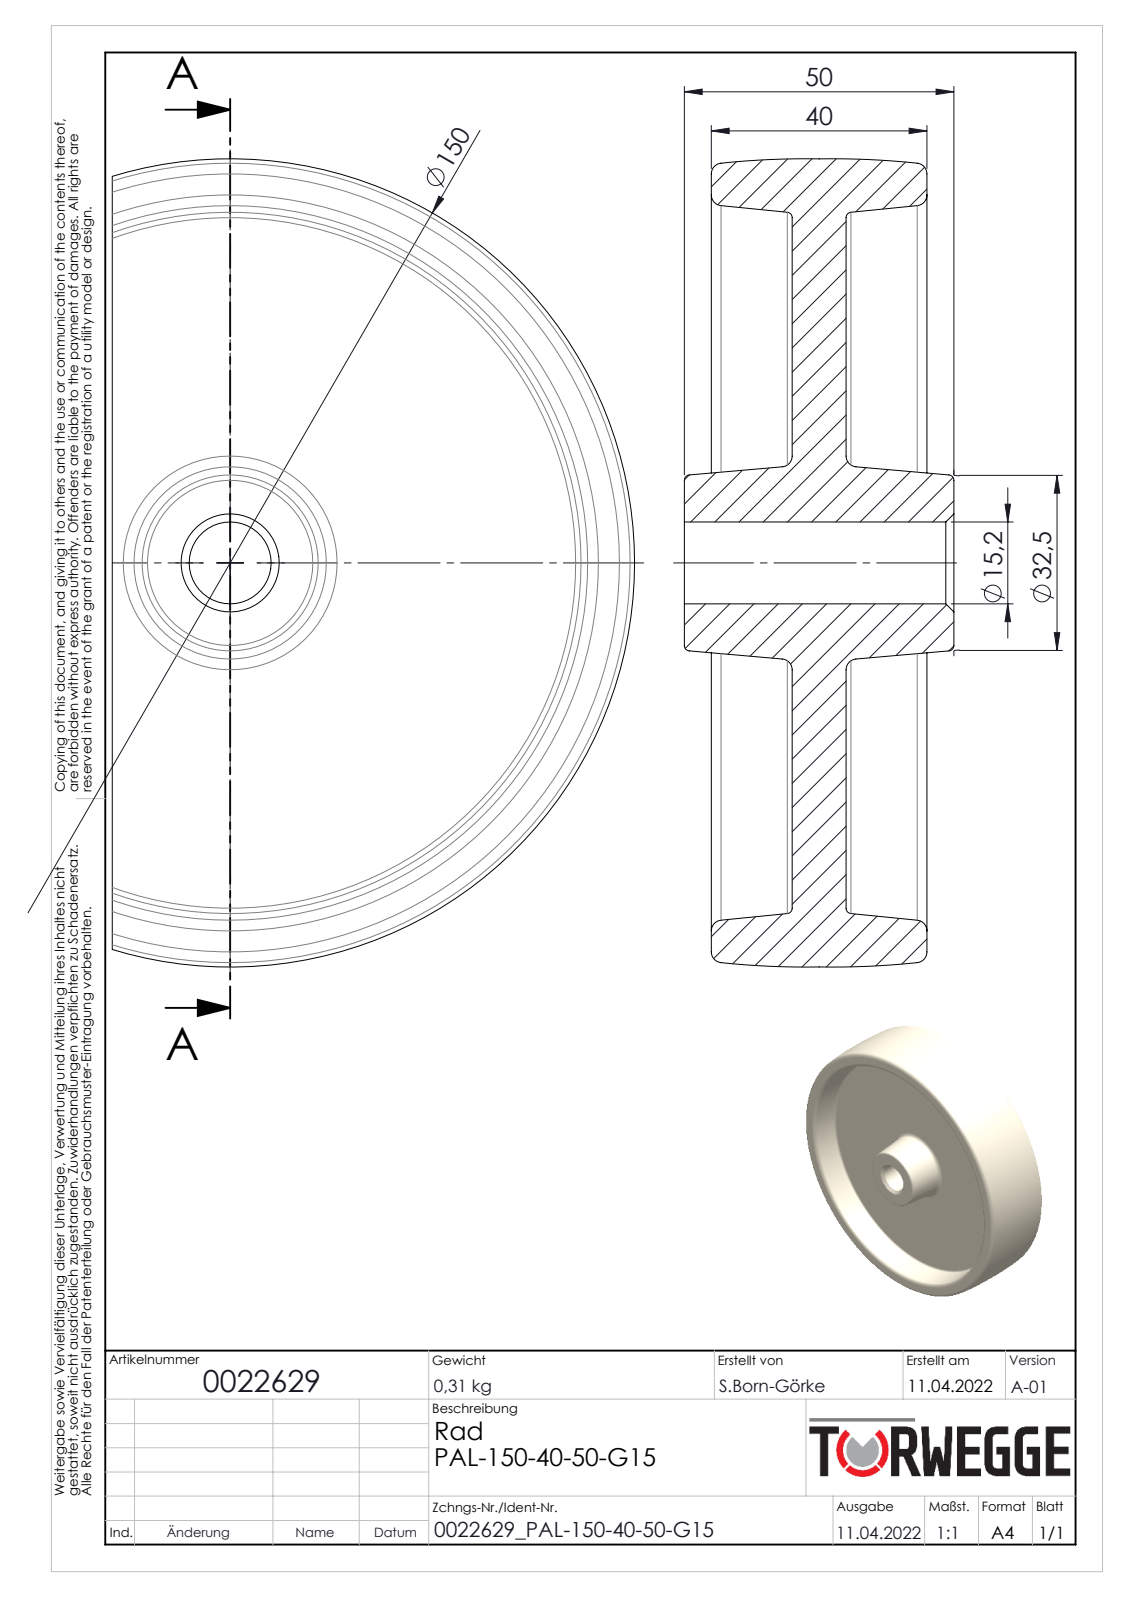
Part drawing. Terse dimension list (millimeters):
name: 0022629
written by: SolidWorks 2020 (AUTOMOTIVE_DESIGN)
unit: mm
bodies: 1 solid, 42 faces (6 planar, 2 cylindrical, 34 other)
size: 150.04 × 150.04 × 50
volume: 321 044 mm³; area: 68 685 mm²
holes: 1× ⌀15.2
face distances: 10, 15, 25, 40, 5, 20, 30, 45, 50
